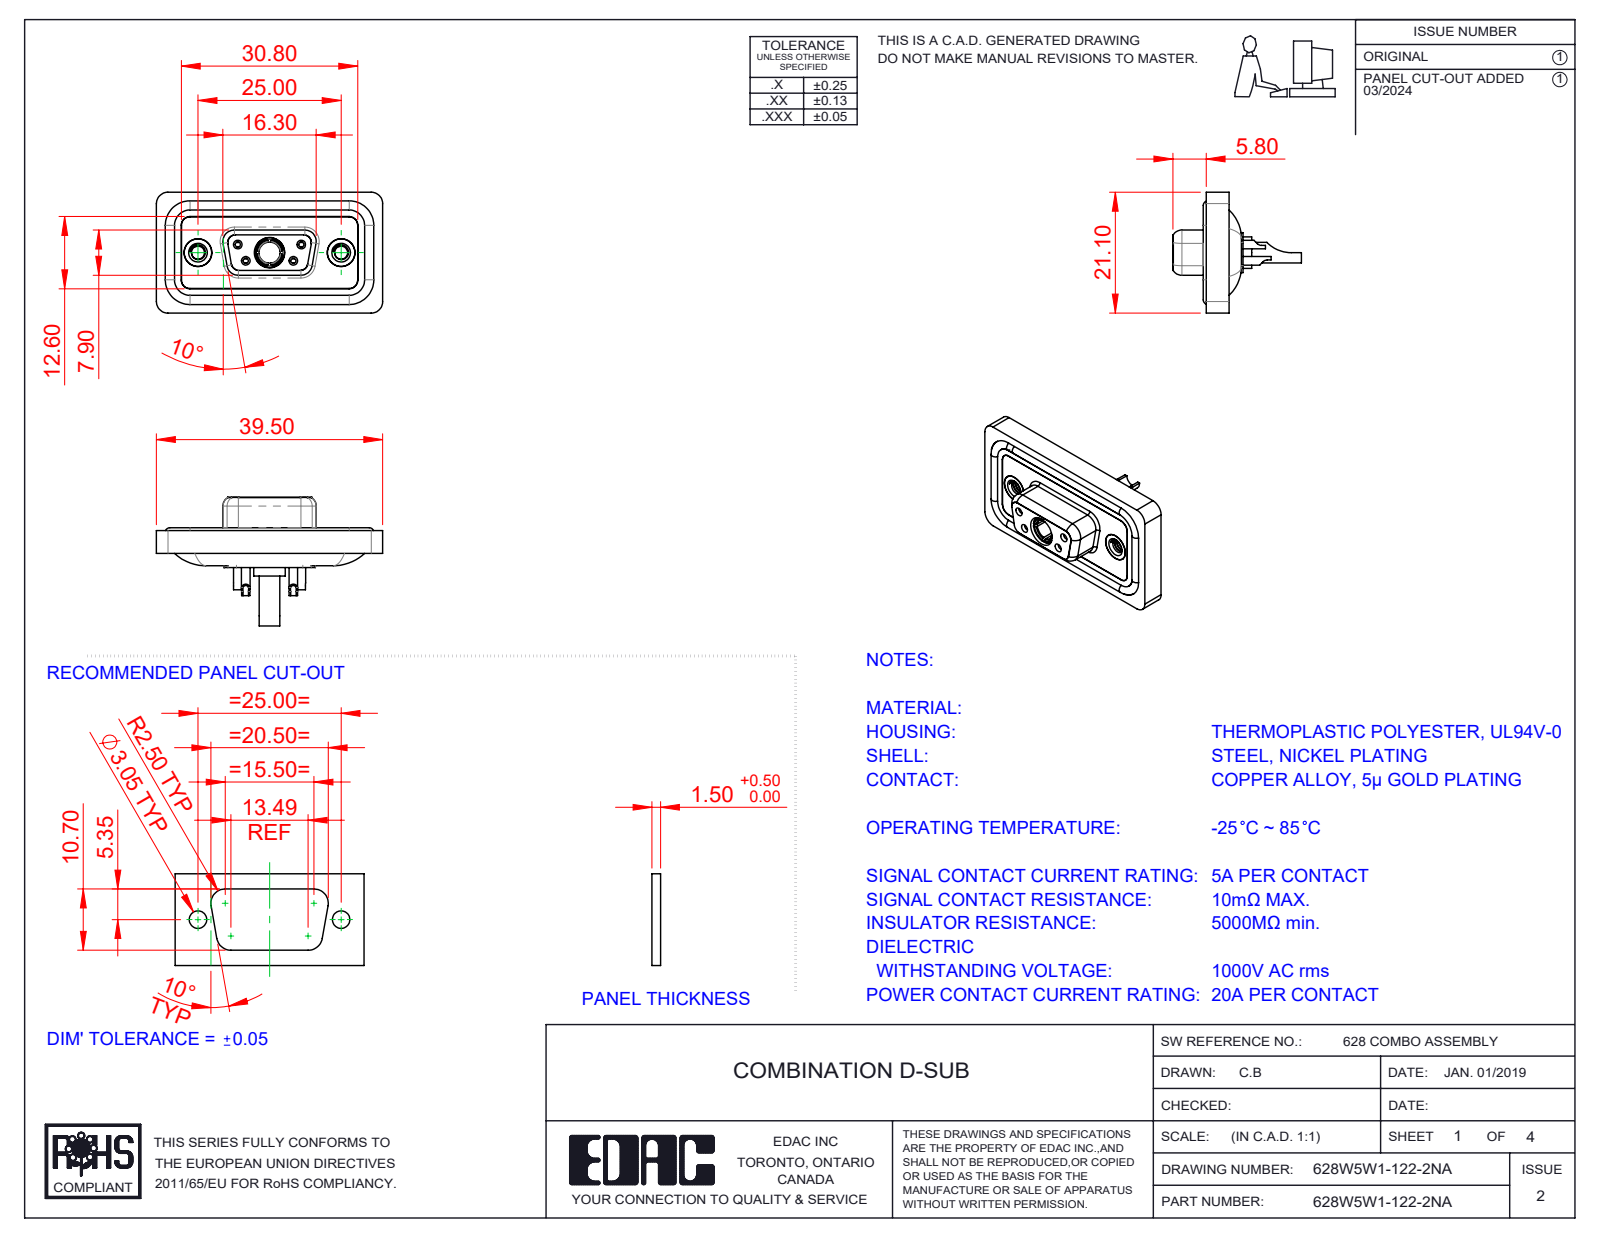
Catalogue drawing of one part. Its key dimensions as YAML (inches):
part_name: "628Combo Shell Front_09 Contacts; 628Combo Waterproof Housing_09 Contacts; 628Combo Threaded Rivet_A; 628Combo Shell Rear_09 Contacts (+5 more)"
step_written_by: "SolidWorks 2023 (CONFIG_CONTROL_DESIGN)"
units: inches
bodies: {solids: 13, faces: 684, planar: 205, cylindrical: 300, other: 179}
overall_size: [1.555, 0.884, 0.831]
volume: 0.292
surface_area: 12.02
round_holes:
  - {diameter: 0.035, count: 4}
  - {diameter: 0.039, count: 4}
  - {diameter: 0.043, count: 4}
  - {diameter: 0.059, count: 4}
  - {diameter: 0.079, count: 4}
  - {diameter: 0.191, count: 3}
  - {diameter: 0.063, count: 2}
  - {diameter: 0.067, count: 2}
  - {diameter: 0.089, count: 2}
  - {diameter: 0.157, count: 2}
  - {diameter: 0.159, count: 2}
  - {diameter: 0.197, count: 2}
round_bosses_or_shafts:
  - {diameter: 0.063, count: 6}
  - {diameter: 0.087, count: 4}
  - {diameter: 0.195, count: 2}
  - {diameter: 0.189, count: 2}
  - {diameter: 0.217, count: 1}
  - {diameter: 0.205, count: 1}
  - {diameter: 0.195, count: 1}
  - {diameter: 0.187, count: 1}
partial_cylinders:
  - {radius: 0.059, count: 22}
  - {radius: 0.079, count: 18}
  - {radius: 0.053, count: 8}
  - {radius: 0.063, count: 8}
  - {radius: 0.039, count: 6}
  - {radius: 0.01, count: 4}
  - {radius: 0.02, count: 4}
  - {radius: 0.024, count: 4}
face_to_face_distances: [0.016, 0.114, 0.043, 0.071, 0.063, 0.02, 0.222, 0.293, 0.211, 0.142]
hole_center_spacings: [0.124, 0.225, 0.28, 0.492, 0.713, 0.173, 0.173, 0.327]
